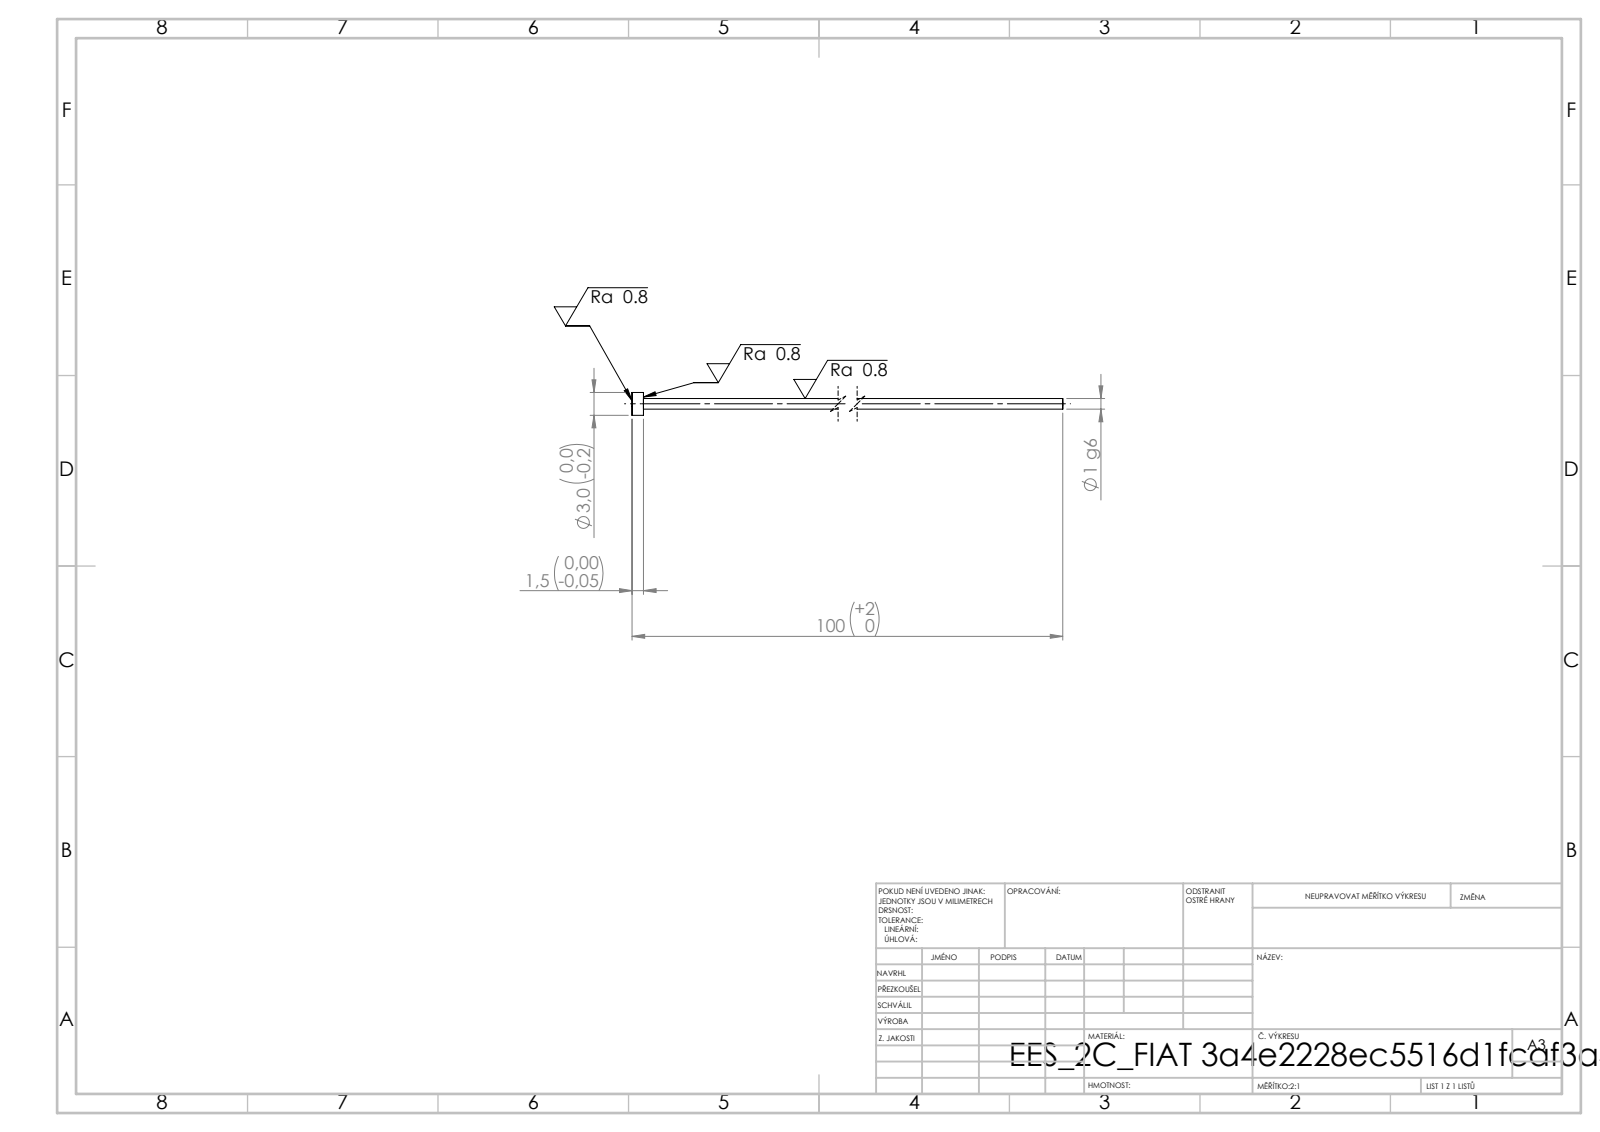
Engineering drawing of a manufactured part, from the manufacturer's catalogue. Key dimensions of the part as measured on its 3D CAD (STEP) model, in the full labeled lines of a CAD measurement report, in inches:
STEP written by: SolidWorks 2019 (CONFIG_CONTROL_DESIGN)
Units: inches
Bodies: 1 solid, 7 faces (3 planar, 4 cylindrical, 0 other)
Overall size (bounding box): 3.937 × 0.118 × 0.118
Volume: 0.01 in³ · Surface area: 0.716 in²
Round bosses / shafts (diameter × count): ⌀0.118 ×1, ⌀0.055 ×1
Main face-to-face distances: 0.059, 3.937, 3.878
